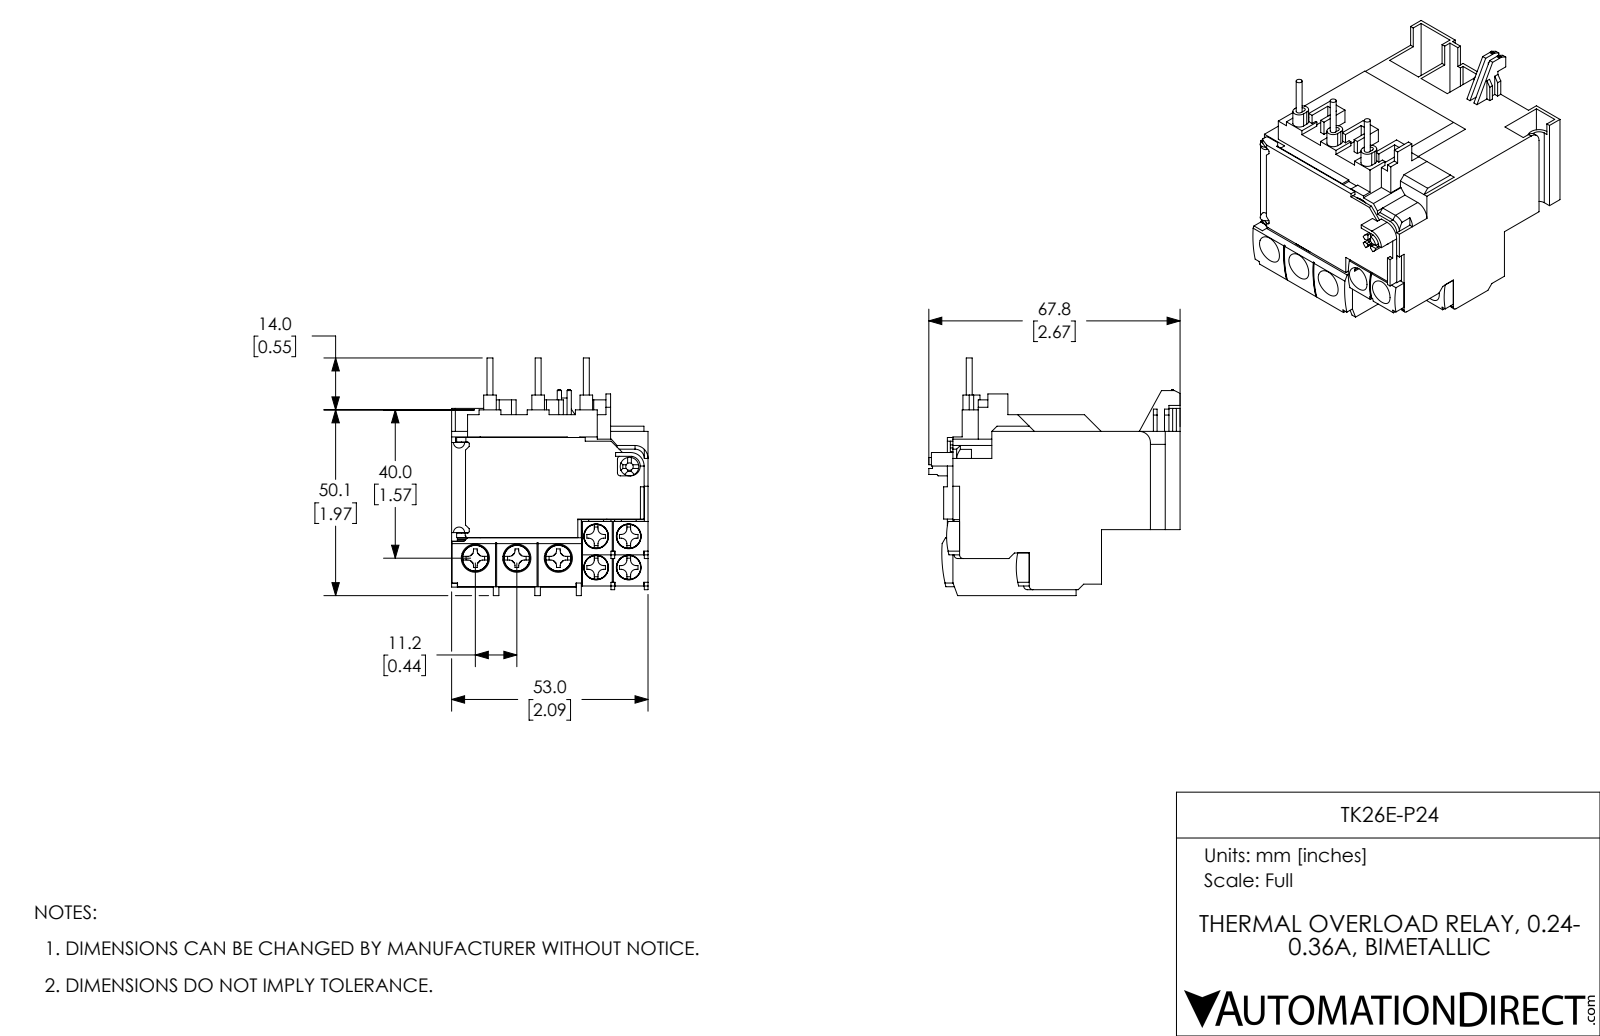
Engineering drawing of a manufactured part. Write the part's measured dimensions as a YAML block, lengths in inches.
part_name: "TK26E-P24"
step_written_by: "SolidWorks 2017 (AUTOMOTIVE_DESIGN)"
units: inches
bodies: {solids: 38, faces: 1480, planar: 1225, cylindrical: 220, other: 35}
overall_size: [2.669, 2.524, 2.087]
volume: 6.099
surface_area: 60.15
round_holes:
  - {diameter: 0.138, count: 4}
  - {diameter: 0.142, count: 4}
  - {diameter: 0.264, count: 4}
  - {diameter: 0.157, count: 3}
  - {diameter: 0.161, count: 3}
  - {diameter: 0.299, count: 3}
  - {diameter: 0.039, count: 1}
  - {diameter: 0.079, count: 1}
  - {diameter: 0.197, count: 1}
  - {diameter: 0.433, count: 1}
round_bosses_or_shafts:
  - {diameter: 0.26, count: 4}
  - {diameter: 0.063, count: 3}
  - {diameter: 0.236, count: 1}
partial_cylinders:
  - {radius: 0.059, count: 28}
  - {radius: 0.039, count: 8}
  - {radius: 0.02, count: 6}
  - {radius: 0.067, count: 6}
  - {radius: 0.031, count: 5}
  - {radius: 0.047, count: 4}
  - {radius: 0.171, count: 4}
  - {radius: 0.189, count: 3}
face_to_face_distances: [0.039, 0.354, 0.059, 0.472, 2.087, 0.079, 0.394, 0.433, 0.343, 0.028]
hole_center_spacings: [0.331, 0.346, 0.441, 0.479, 0.376, 0.413, 0.464, 0.74]
